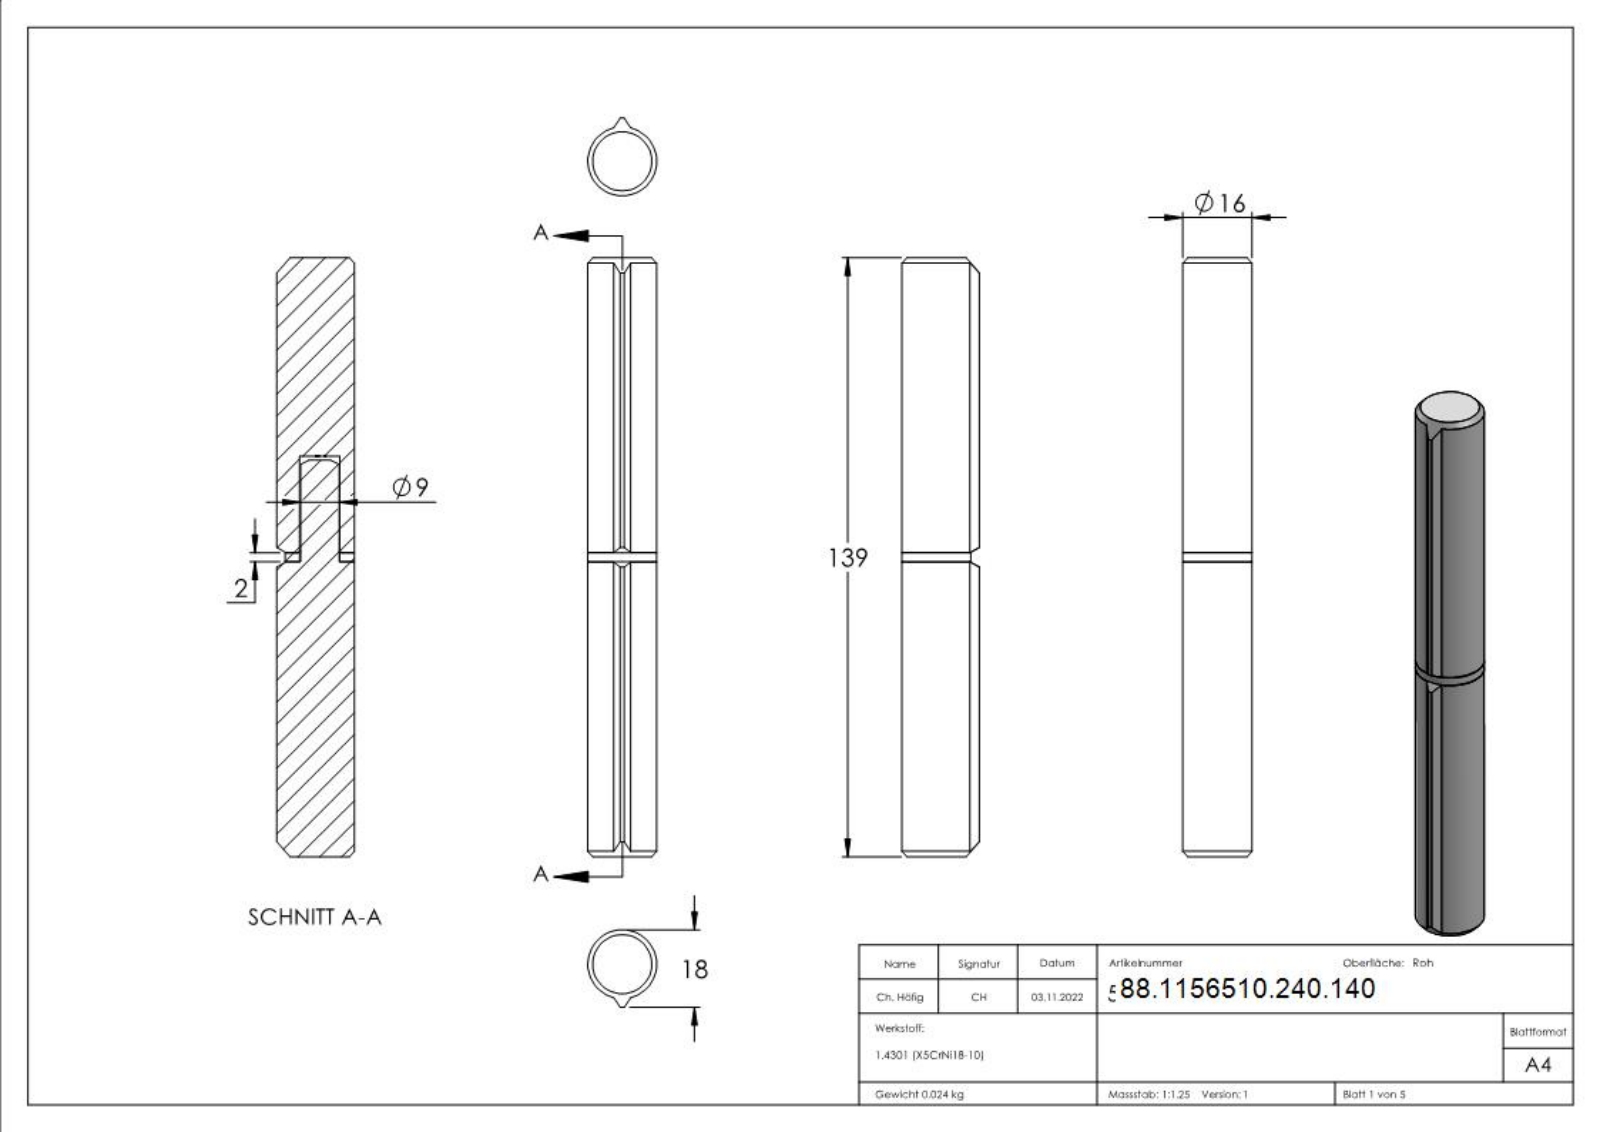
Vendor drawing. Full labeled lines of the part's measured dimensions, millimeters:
Part name (STEP PRODUCT): 56510-240 Teil2_56510-240-140 Teil2; 56510-240 Teil1_56510-240-140 Teil1; 56510-240-140; 56510-240 Teil3_56510-240-140 Teil3
STEP written by: SolidWorks 2018 (CONFIG_CONTROL_DESIGN)
Units: millimetres
Bodies: 3 solids, 326 faces (188 planar, 6 cylindrical, 132 other)
Overall size (bounding box): 139 × 18 × 16
Volume: 28 330 mm³ · Surface area: 9 643 mm²
Round holes (diameter × count): ⌀9.3 ×1
Round bosses / shafts (diameter × count): ⌀16 ×1, ⌀9 ×1
Main face-to-face distances: 68.5, 70.5, 2, 139, 93, 24.5, 22.5, 46, 1, 92
